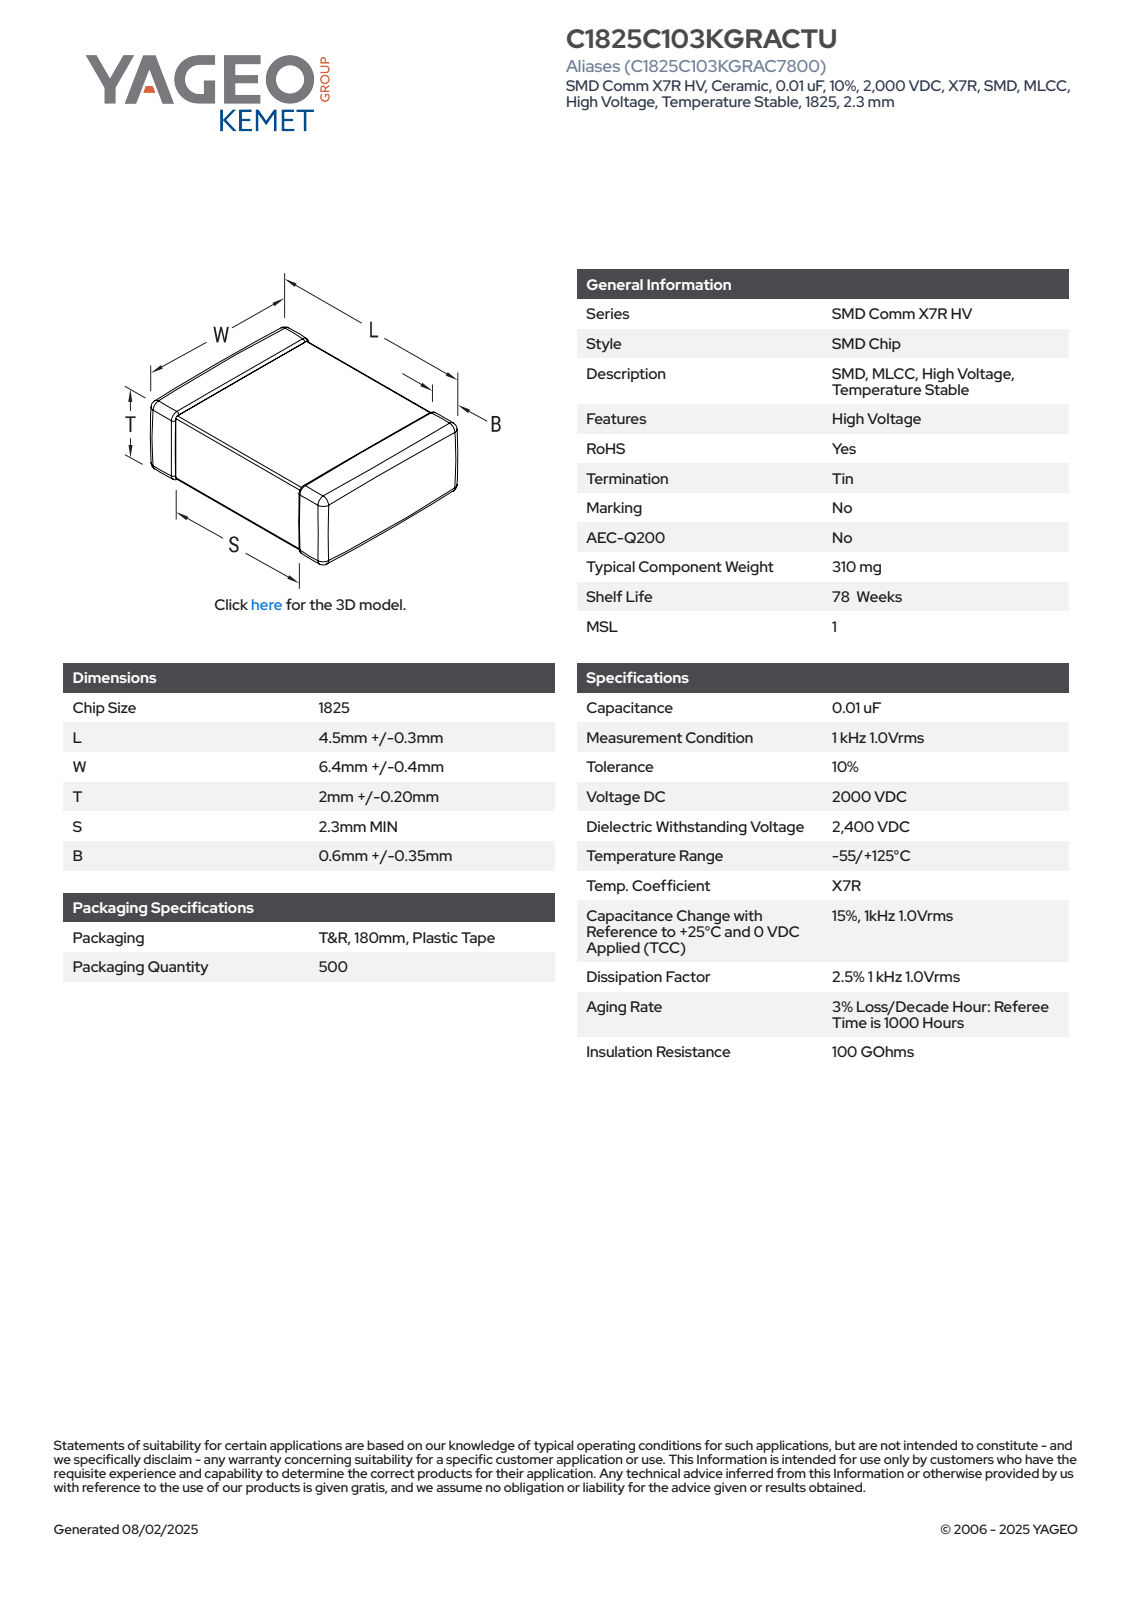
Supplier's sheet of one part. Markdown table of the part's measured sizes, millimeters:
| quantity | value |
| --- | --- |
| part name | CCS_CCSTD_1825_L4.8W6.8T2.2B0.6 |
| STEP written by | SolidWorks 2021 (AUTOMOTIVE_DESIGN) |
| units | millimeters |
| bodies | 4 solids, 125 faces (71 planar, 38 cylindrical, 16 other) |
| overall size | 6.8 × 4.8 × 2.2 |
| volume | 64 mm³ |
| surface area | 118 mm² |
| partial cylindrical surfaces (radius × count) | 0.14 × 24 |
| main face-to-face distances | 1.92, 2.06, 4.8, 2.2, 6.66, 6.52, 6.8, 1.59, 3.21, 2.59 |
